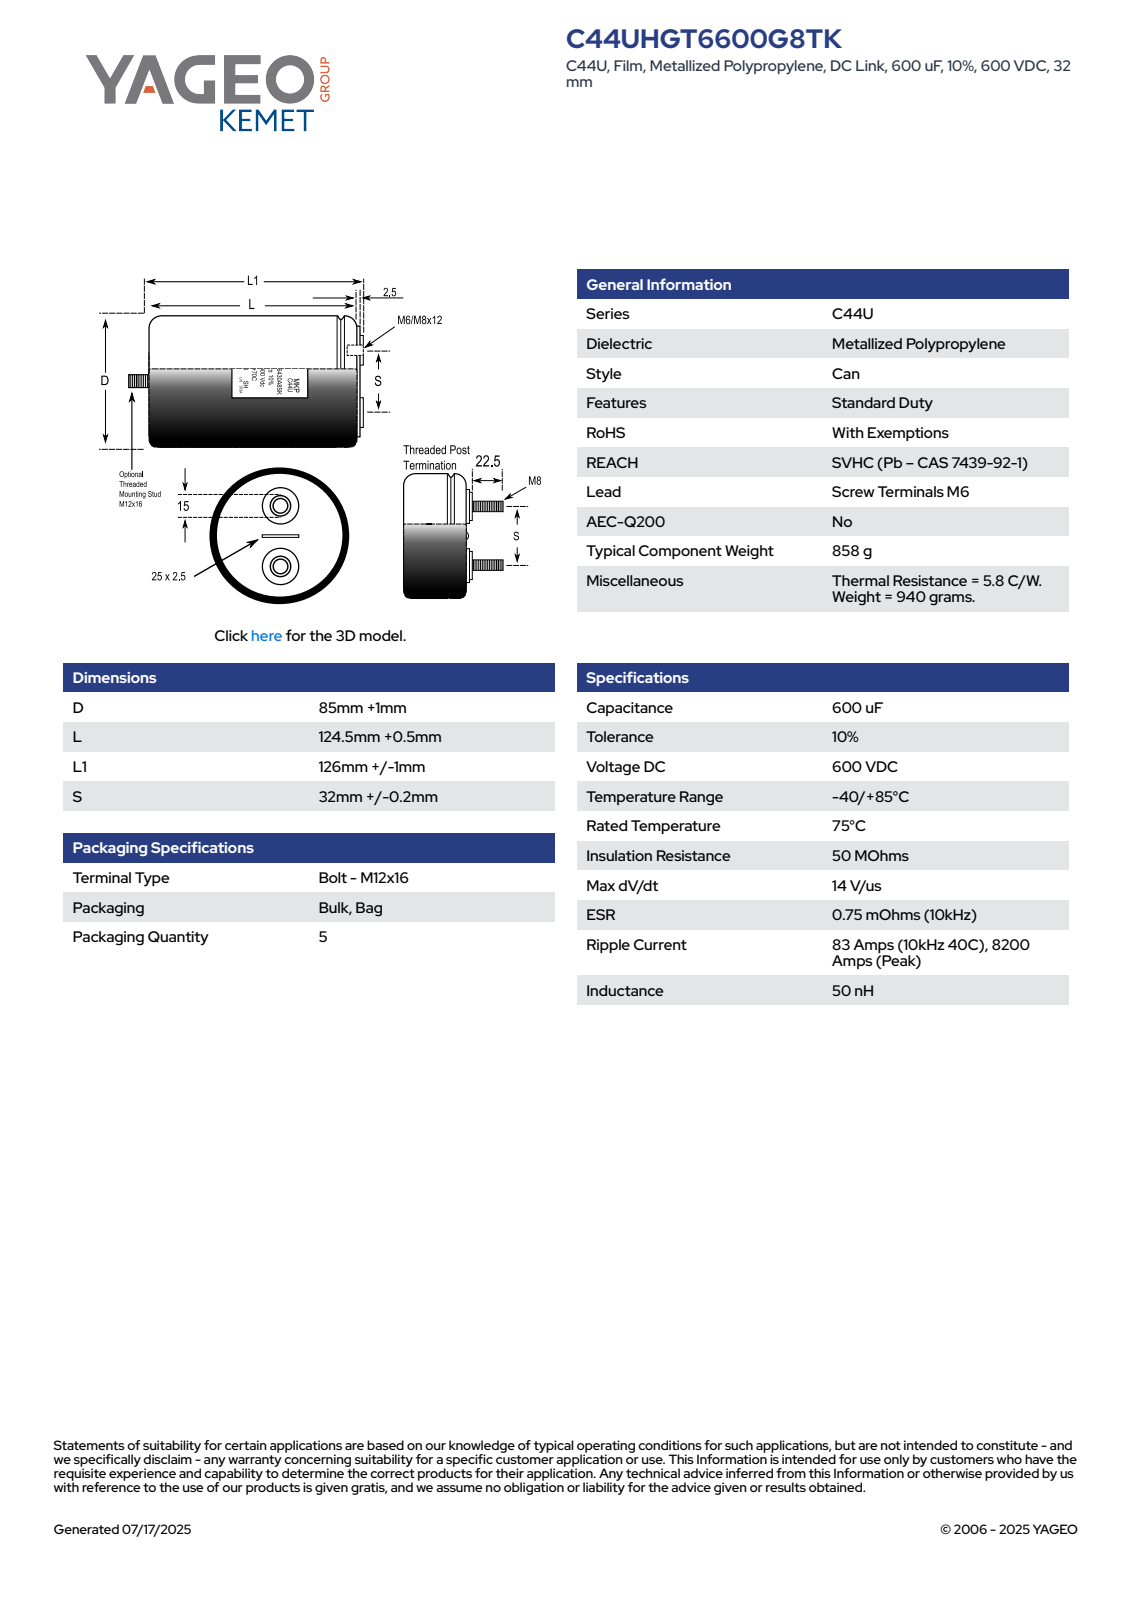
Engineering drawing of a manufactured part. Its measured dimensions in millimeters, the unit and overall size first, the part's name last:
Units: millimetres
Overall size (bounding box): 145 × 86 × 86
Round holes (diameter × count): ⌀6 ×2
Round bosses / shafts (diameter × count): ⌀18 ×2, ⌀15 ×2, ⌀86 ×1, ⌀70 ×1, ⌀12 ×1
Partial cylindrical surfaces — rounded edges, fillets, slot ends (radius × count): R42.99 ×1
Main face-to-face distances: 126.51, 129, 2.49, 127.75, 1.24, 1.25, 16, 142.51, 143.75, 145
Hole centre spacings: 32.2
Volume: 729 168 mm³ · Surface area: 45 531 mm²
Bodies: 1 solid, 104 faces (36 planar, 29 cylindrical, 39 other)
Part name (STEP PRODUCT): CFP_C44U_T_85X124.5_D86L126.5S32.2
STEP written by: SolidWorks 2014 (AUTOMOTIVE_DESIGN)
